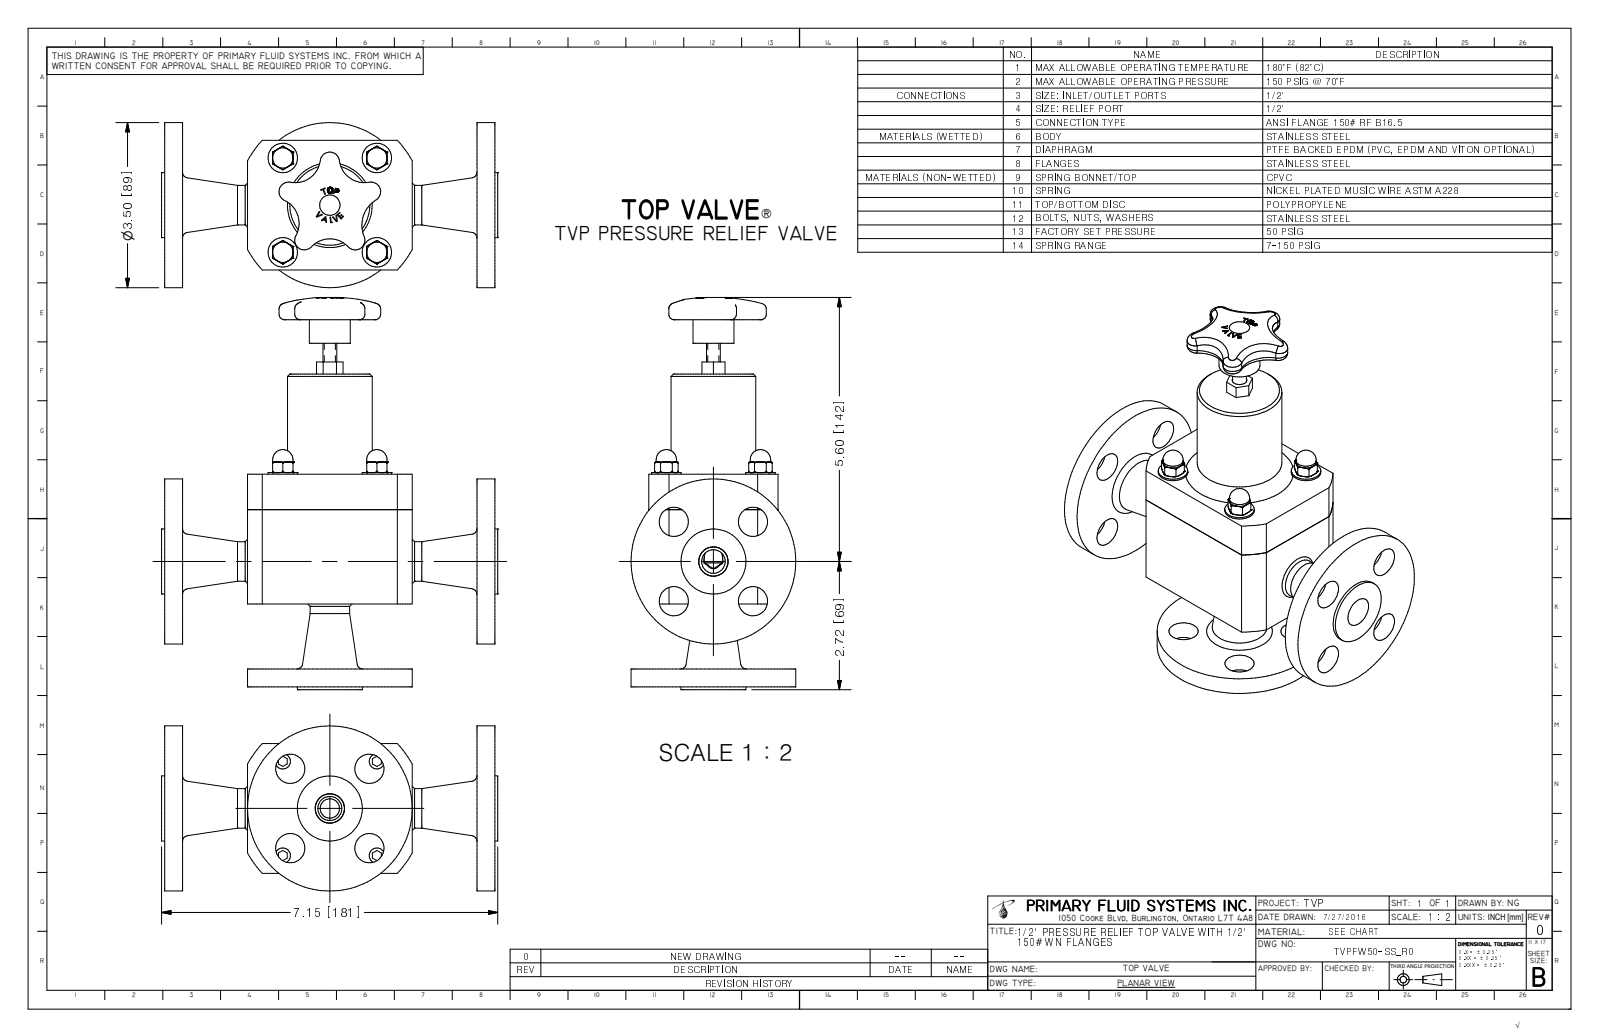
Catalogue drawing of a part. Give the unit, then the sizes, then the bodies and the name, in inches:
Units: inches
Overall size (bounding box): 8.319 × 7.145 × 3.5
Round holes (diameter × count): ⌀0.62 ×8, ⌀0.175 ×4, ⌀0.622 ×2, ⌀2.4 ×1
Round bosses / shafts (diameter × count): ⌀0.625 ×4, ⌀0.433 ×4, ⌀3.5 ×2, ⌀1.38 ×2, ⌀0.84 ×2, ⌀2.375 ×1, ⌀1.8 ×1, ⌀0.87 ×1
Partial cylindrical surfaces — rounded edges, fillets, slot ends (radius × count): R0.085 ×5, R0.205 ×5, R0.536 ×4, R0.656 ×4, R0.625 ×1, R0.745 ×1, R1.988 ×1
Main face-to-face distances: 0.38, 6.64, 2.75, 1.757, 7.02, 1.377, 6.26, 5.257, 4.878, 1.383
Hole centre spacings: 1.19, 1.683, 1.848, 0.224, 1.414, 2, 2.38, 2.604
Volume: 44.22 in³ · Surface area: 168 in²
Bodies: 1 solid, 352 faces (132 planar, 65 cylindrical, 155 other)
Part name (STEP PRODUCT): TVPFW50-SS_R0
STEP written by: Autodesk Inventor 2009 (AUTOMOTIVE_DESIGN)
